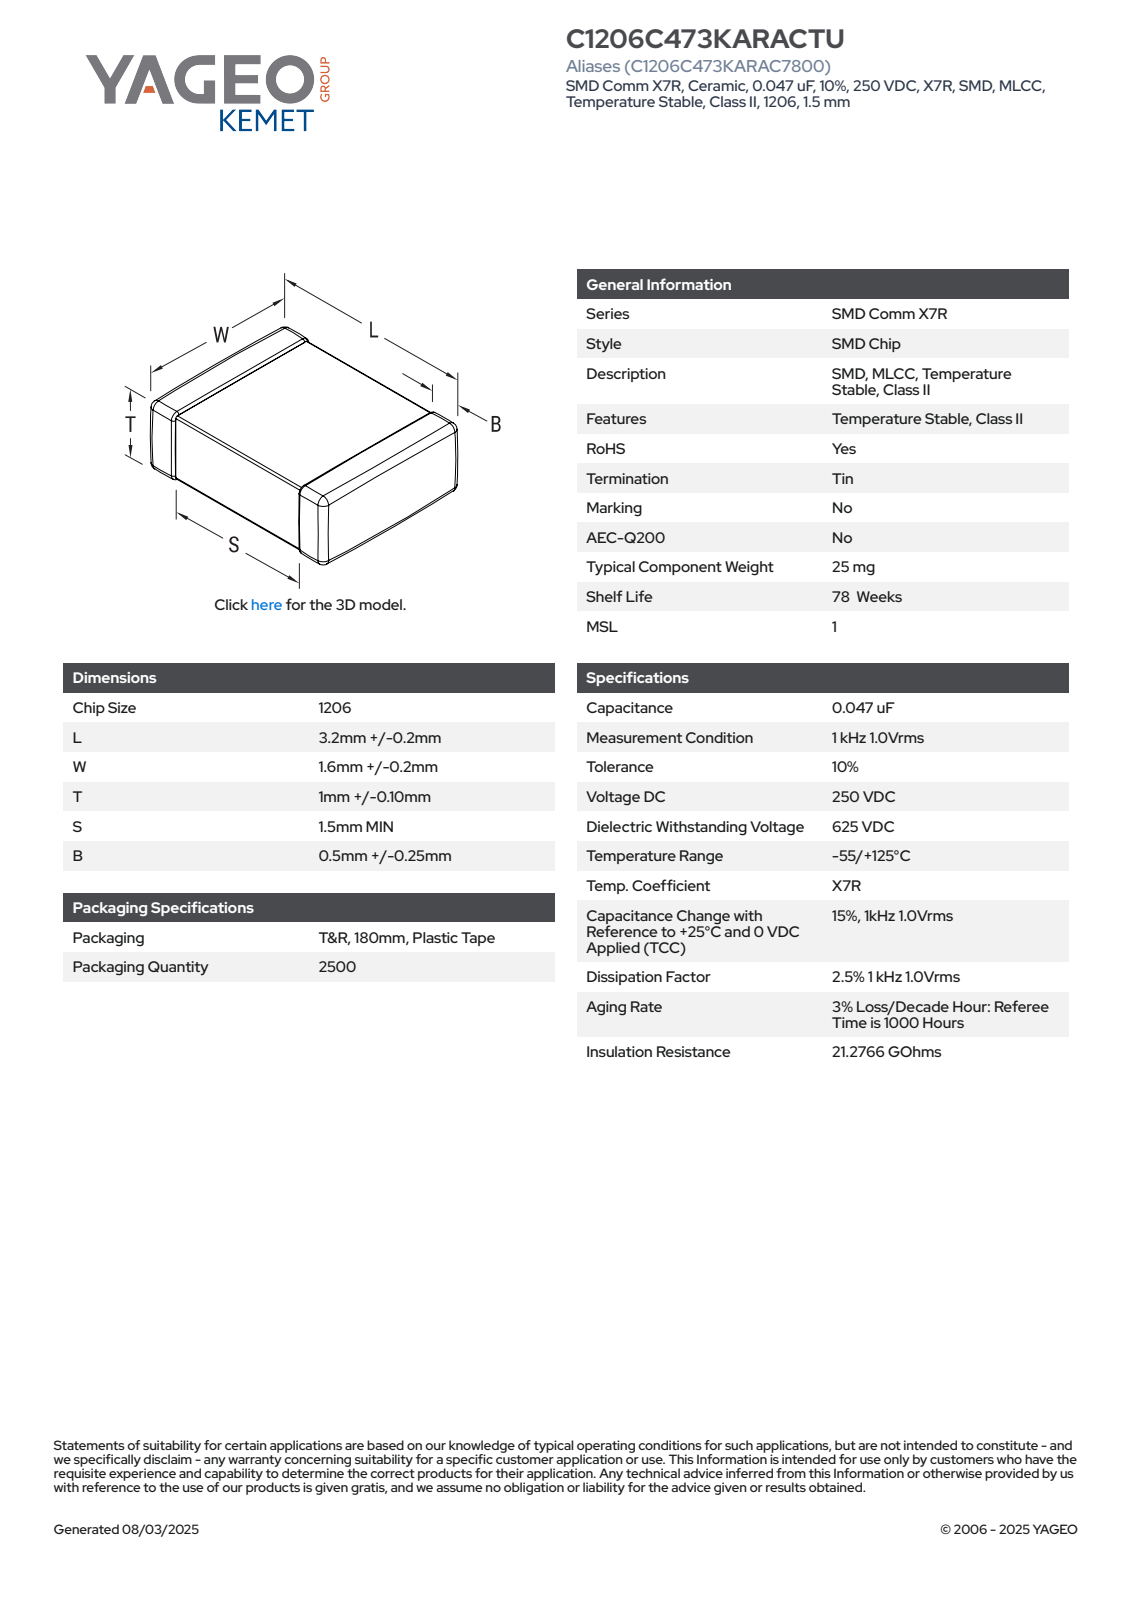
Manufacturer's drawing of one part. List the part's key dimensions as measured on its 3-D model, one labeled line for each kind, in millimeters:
Part name (STEP PRODUCT): CCS_CCSTDNOS_1206_L3.4W1.8T1.1B0.75
STEP written by: SolidWorks 2014 (AUTOMOTIVE_DESIGN)
Units: millimetres
Bodies: 4 solids, 125 faces (71 planar, 38 cylindrical, 16 other)
Overall size (bounding box): 3.4 × 1.8 × 1.1
Volume: 6 mm³ · Surface area: 23 mm²
Main face-to-face distances: 1.06, 1.02, 1.76, 1.1, 1.72, 3.4, 1.8, 1.03, 1.07, 0.99
